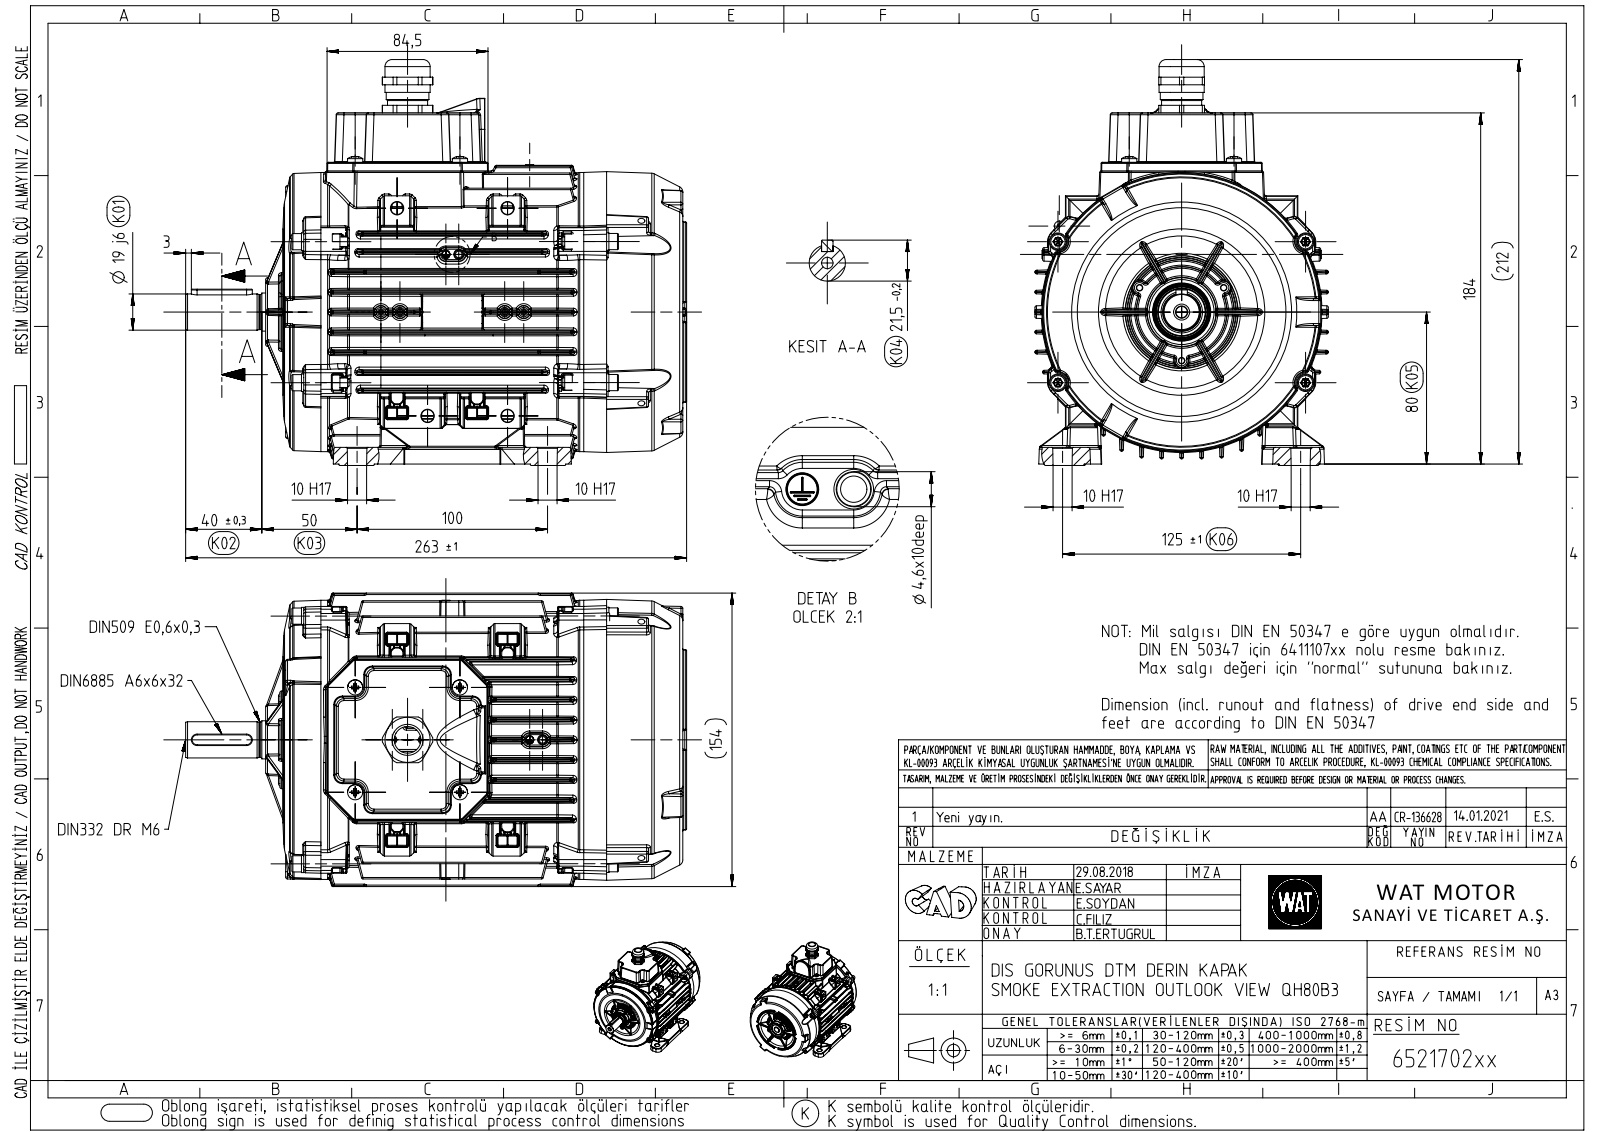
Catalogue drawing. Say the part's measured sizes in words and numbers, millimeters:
The part is named "2603BE5CCA1Ccx5m". Its 3-D file was written by "SIEMENS PLM Software NX 11.0 (AUTOMOTIVE_DESIGN)". It is 0 solids with 6405 faces: 1138 planar, 1739 cylindrical and 3528 other. Overall it measures 263 by 213 by 154 millimeters. Round holes: 4 of diameter 3.7, 3 of diameter 3, 1 of diameter 3.99, 1 of diameter 6.4, 1 of diameter 14, 1 of diameter 24, 1 of diameter 27.8, 1 of diameter 28, 1 of diameter 30. Round bosses or shafts: 8 of diameter 8.5, 8 of diameter 5, 4 of diameter 9.2, 4 of diameter 8, 1 of diameter 146.5, 1 of diameter 29.5, 1 of diameter 23.7, 1 of diameter 22.4. Partial cylindrical surfaces (rounded edges, fillets, slot ends): 443 of radius 0.5, 361 of radius 1, 328 of radius 0.8, 65 of radius 0.2, 29 of radius 2, 17 of radius 5, 8 of radius 4, 8 of radius 8. The main face-to-face distances are 41.96, 10.36, 20.98, 52.32, 59.48, 10.49, 10.48, 20.84, 31.48, 7.16. The hole center spacings are 25.5, 20, 44.17, 25.4, 25.52, 25.57, 44.16.
